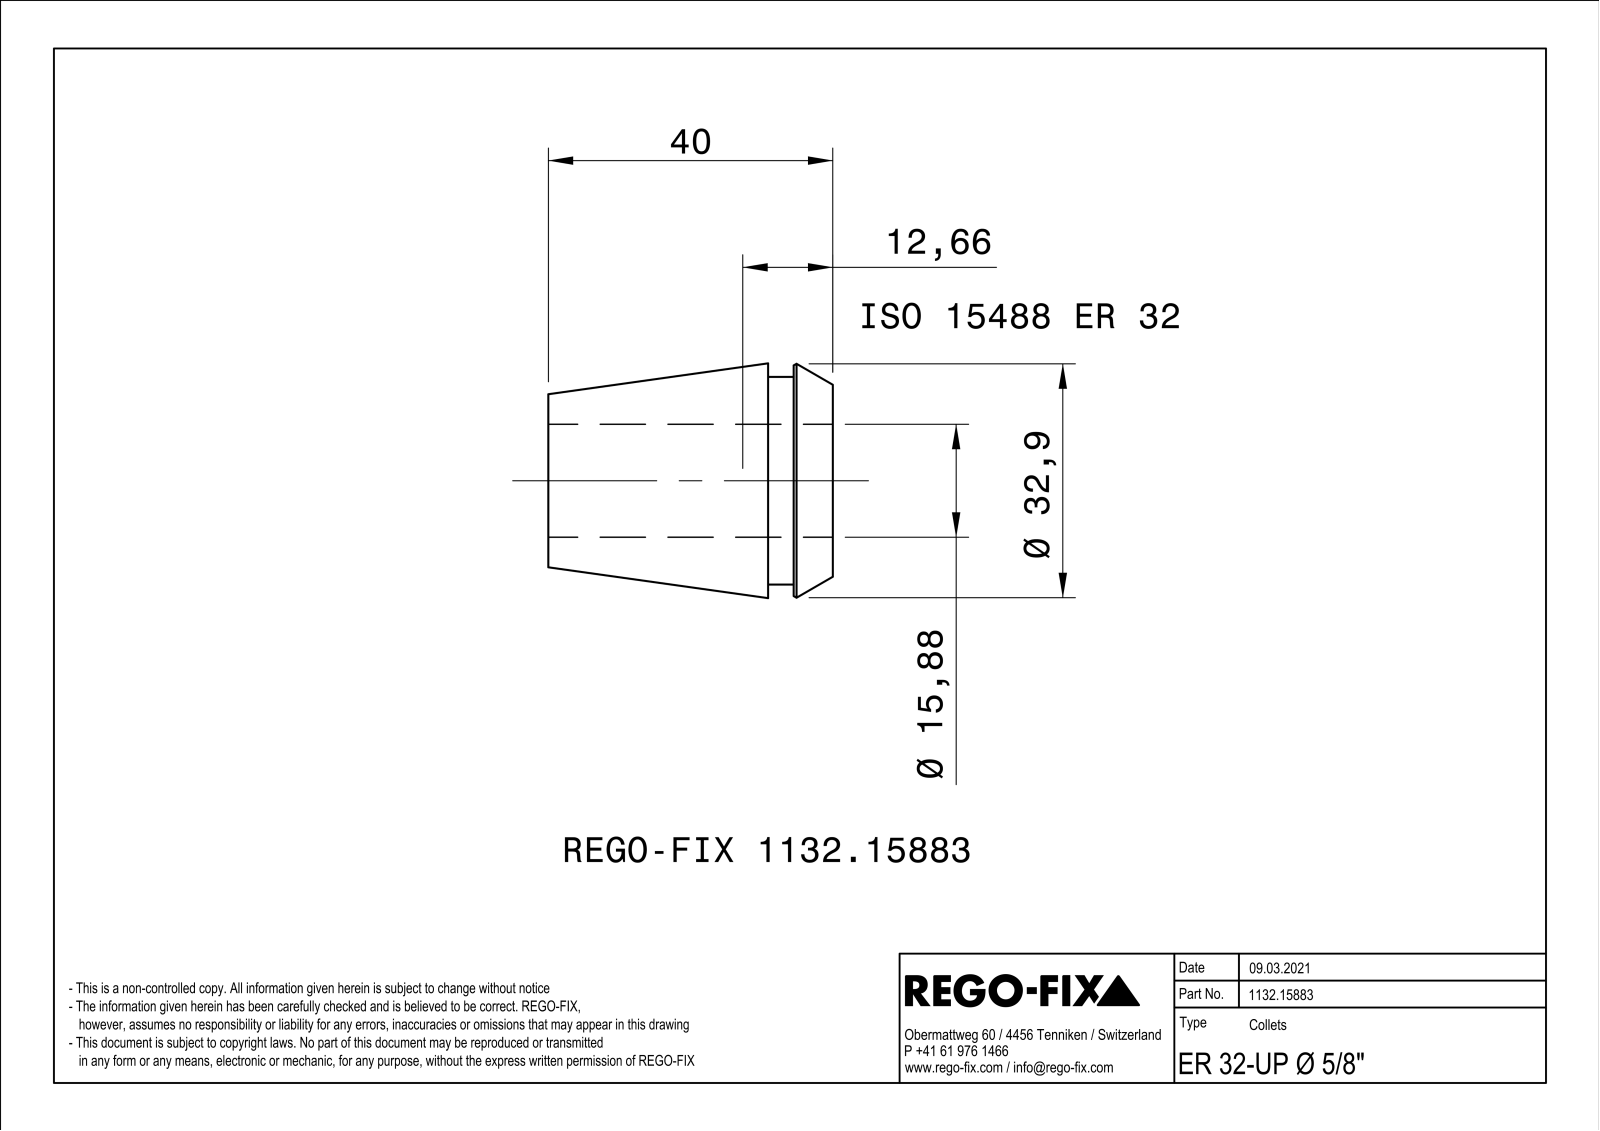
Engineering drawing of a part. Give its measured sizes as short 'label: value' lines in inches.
name: NOCUT
written by: SIEMENS PLM Software Solid Edge ST10 (AUTOMOTIVE_DESIGN)
unit: in
bodies: 1 solid, 209 faces (88 planar, 41 cylindrical, 80 other)
size: 1.575 × 1.298 × 1.298
volume: 0.903 in³; area: 20.05 in²
holes: 1× ⌀0.625
bosses: 1× ⌀1.15
rounds: 20× R0.016
face distances: 0.039, 1.575, 0.358, 1.217, 0.217, 0.142, 1.358, 0.236, 0.02, 0.122
